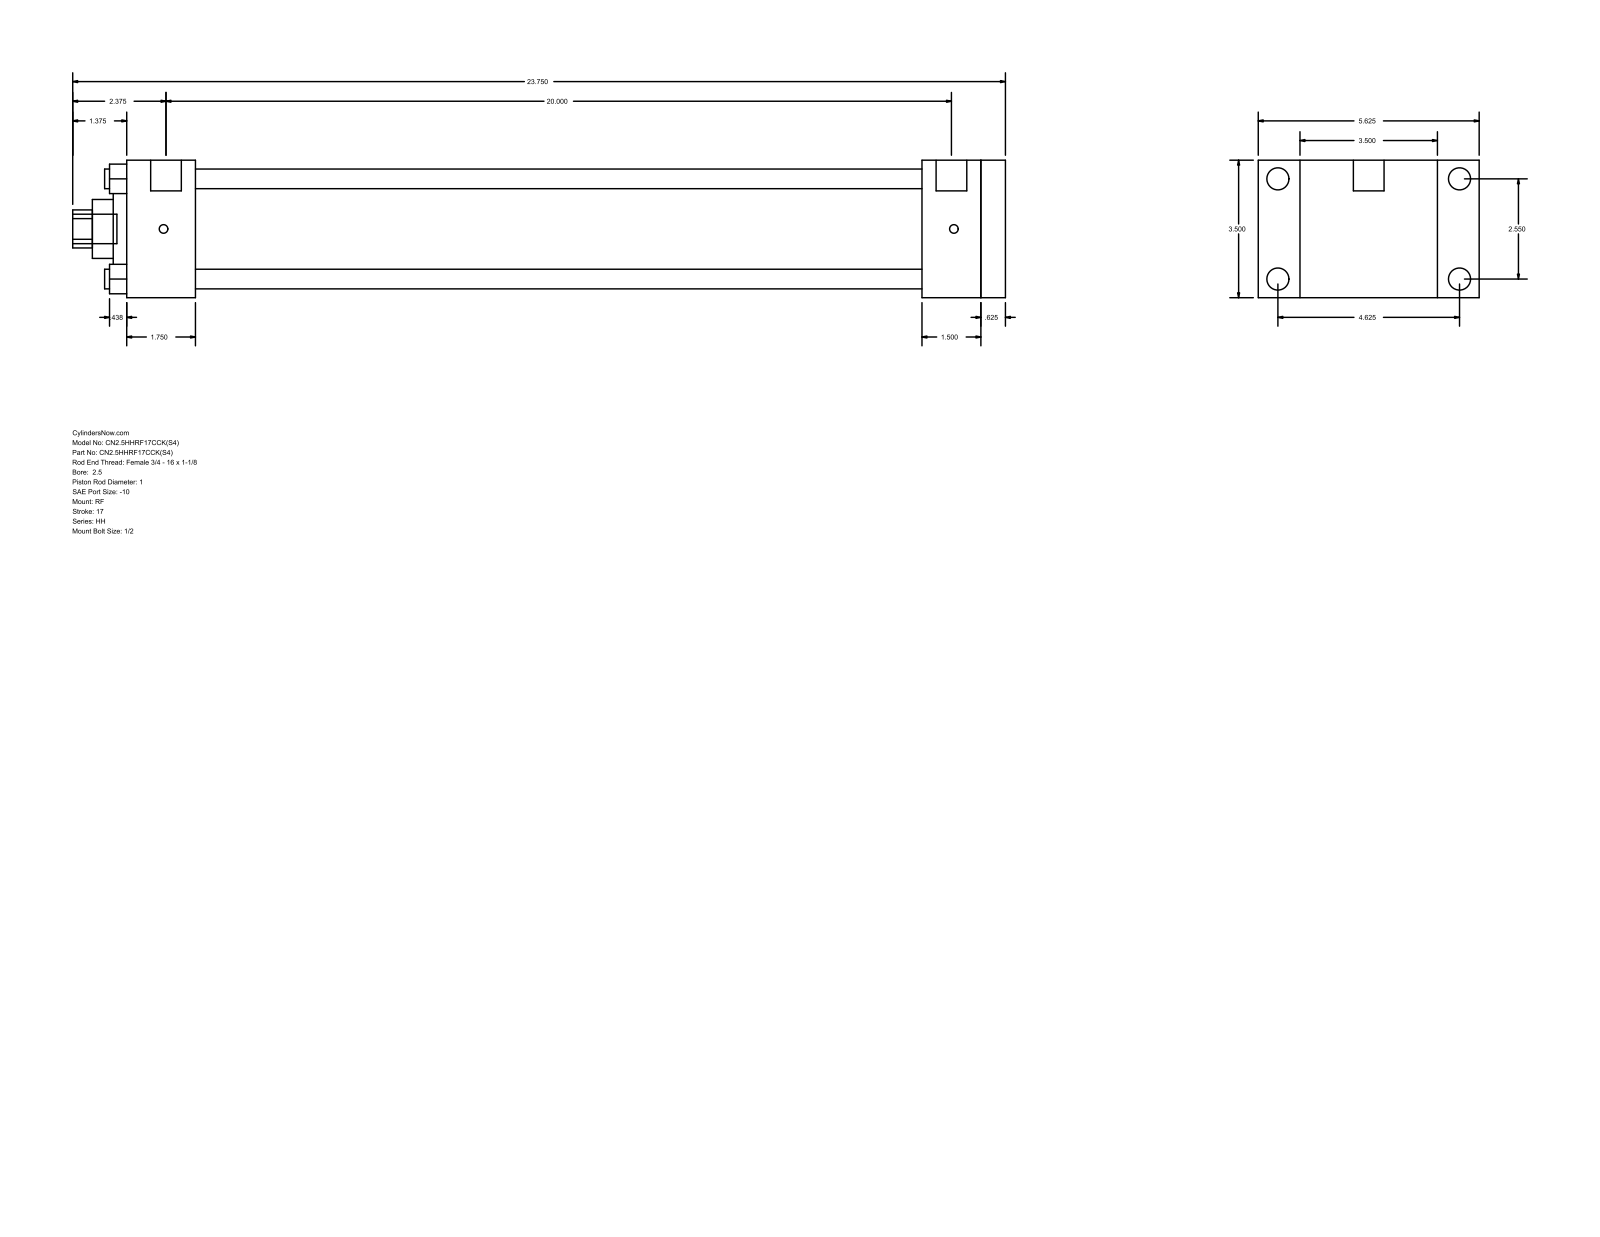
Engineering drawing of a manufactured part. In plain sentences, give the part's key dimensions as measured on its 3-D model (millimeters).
The part is named "HH_RF__0250_1". Its 3-D file was written by "GSSL Pune (CONFIG_CONTROL_DESIGN)". It is 0 solids with 94 faces: 65 planar, 29 cylindrical and 0 other. Overall it measures 603.25 by 142.88 by 88.9 millimeters. Round holes: 4 of diameter 12.7, 1 of diameter 25.4, 1 of diameter 38.1, 1 of diameter 60.33, 1 of diameter 73.03. Round bosses or shafts: 4 of diameter 14.3, 4 of diameter 5.56, 2 of diameter 19.84, 1 of diameter 19.05. Partial cylindrical surfaces (rounded edges, fillets, slot ends): 1 of radius 12.29. The main face-to-face distances are 88.9, 15.87, 552.46, 568.33, 44.46, 508, 523.87, 514.35, 469.89, 38.11. The hole center spacings are 45.79, 64.76, 91.58.
